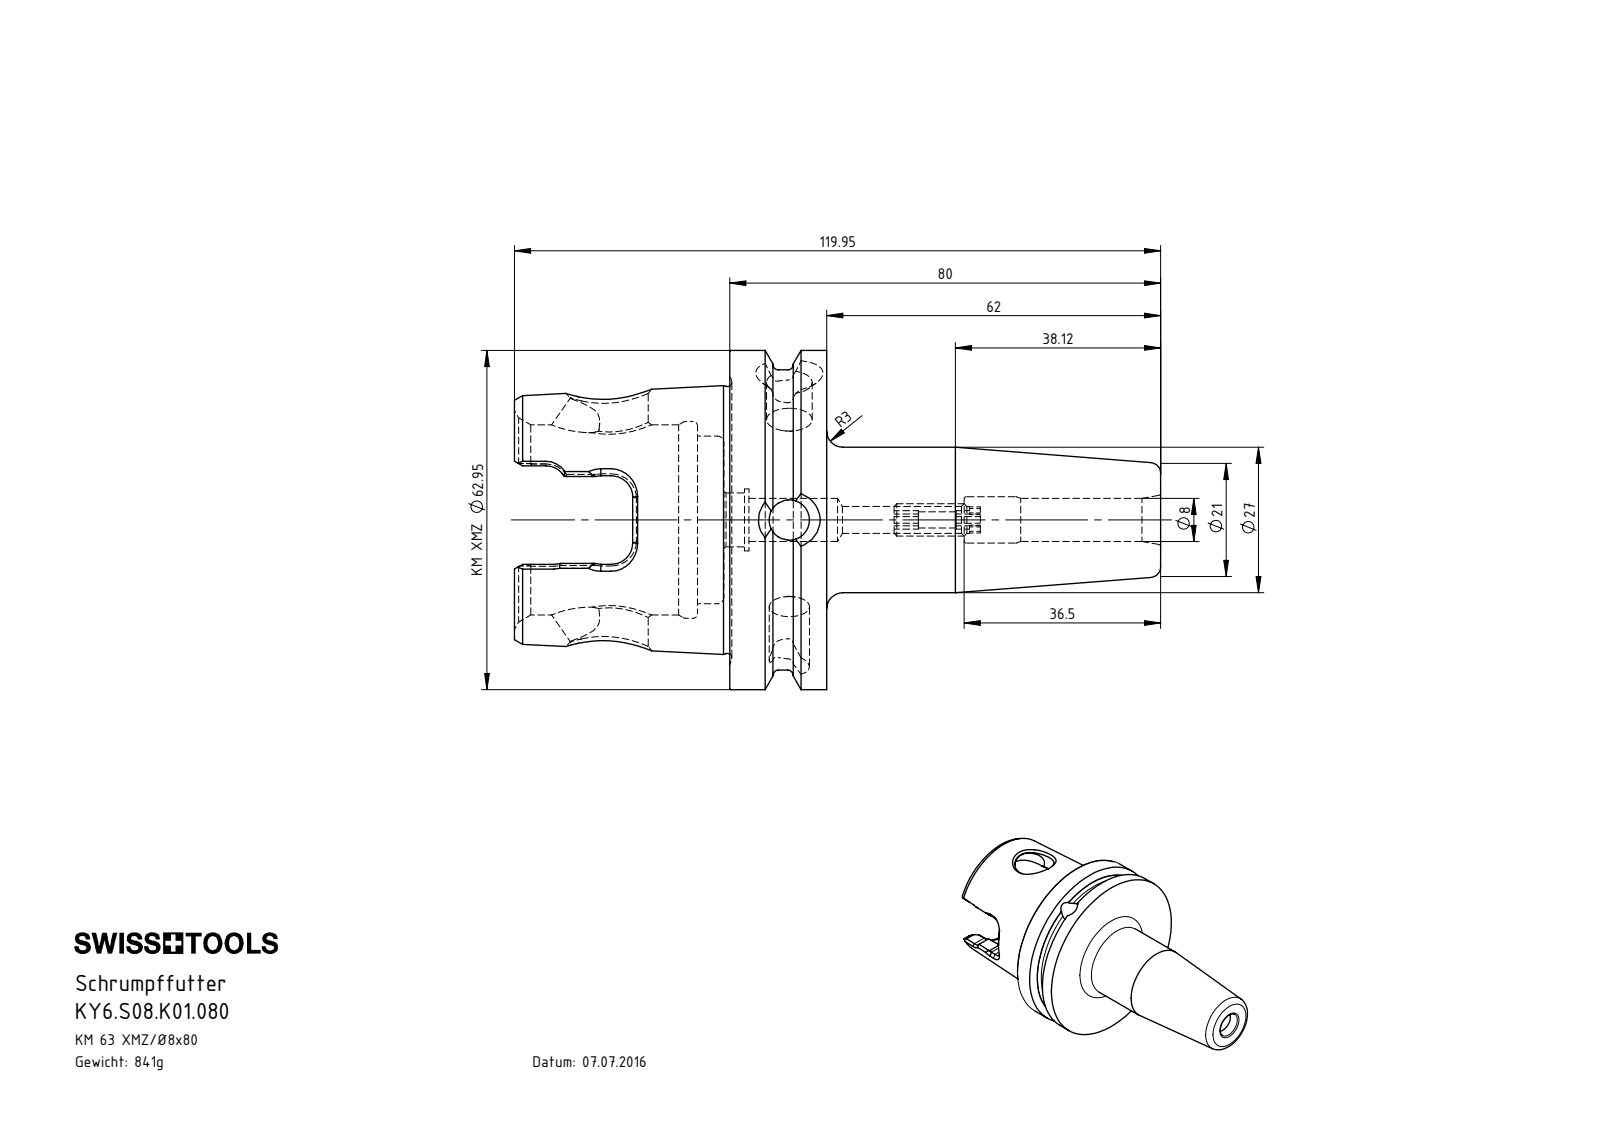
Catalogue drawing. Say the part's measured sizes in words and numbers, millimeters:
The part is named "KY6-S08.K01.080; ERU-AN2.K01.016_A; KY6-S08.K01.080_A". Its 3-D file was written by "SolidWorks 2012 (CONFIG_CONTROL_DESIGN)". It is 2 solids with 272 faces: 79 planar, 60 cylindrical and 133 other. Overall it measures 119.95 by 62.95 by 62.95 millimeters. Its volume is 107 104 cubic millimeters and its surface area 26 558 square millimeters. Round holes: 2 of diameter 7.47, 1 of diameter 3, 1 of diameter 5, 1 of diameter 8, 1 of diameter 8.48, 1 of diameter 8.6, 1 of diameter 10, 1 of diameter 11.5, 1 of diameter 14.5, 1 of diameter 31.1, 1 of diameter 35.27, 1 of diameter 36.5. Round bosses or shafts: 1 of diameter 62.95, 1 of diameter 55.7, 1 of diameter 27, 1 of diameter 6. Partial cylindrical surfaces (rounded edges, fillets, slot ends): 6 of radius 4, 2 of radius 7.04. The main face-to-face distances are 18, 1.1, 19.1, 39.95, 24, 4.9, 6, 33.95, 38.85, 57.95.
